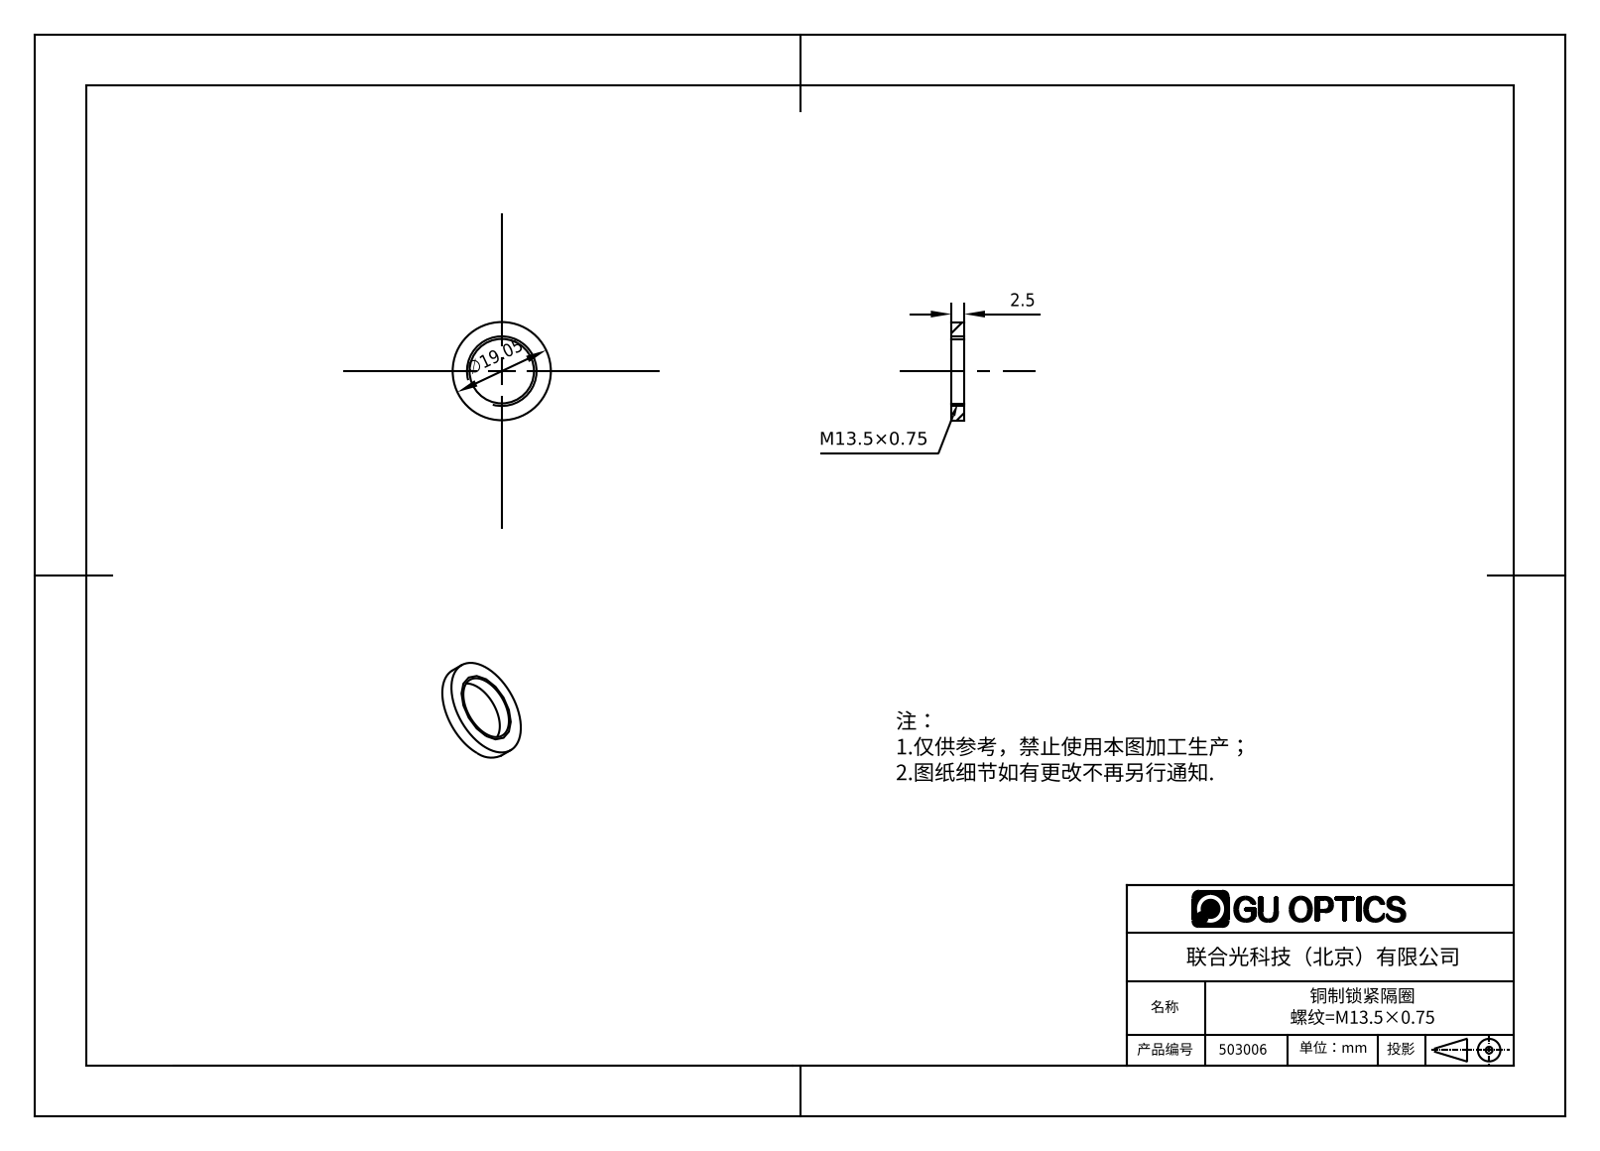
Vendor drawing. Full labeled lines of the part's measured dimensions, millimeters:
Part name (STEP PRODUCT): 511006
STEP written by: SolidWorks 2016 (AUTOMOTIVE_DESIGN)
Units: millimetres
Bodies: 1 solid, 6 faces (2 planar, 4 cylindrical, 0 other)
Overall size (bounding box): 19.05 × 19.05 × 2.5
Volume: 406 mm³ · Surface area: 572 mm²
Round holes (diameter × count): ⌀12.5 ×1
Round bosses / shafts (diameter × count): ⌀19.05 ×1
Main face-to-face distances: 2.5
